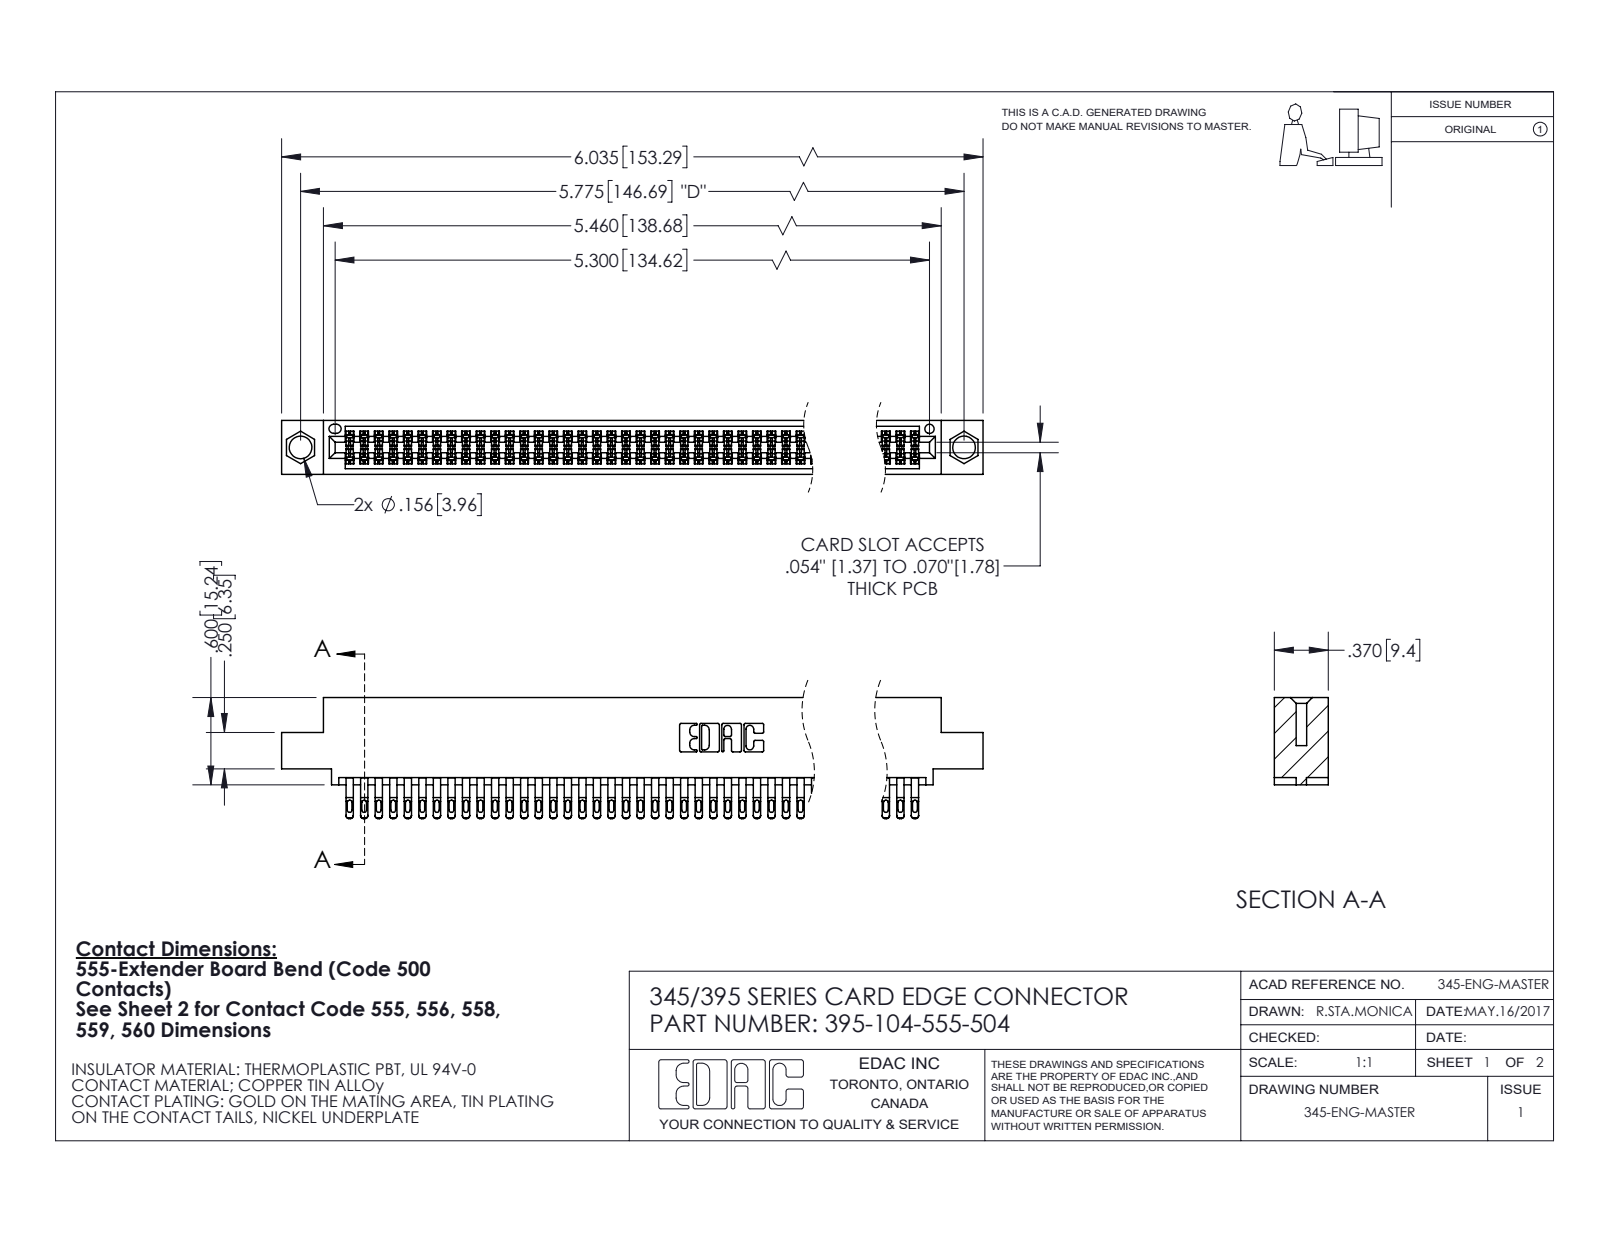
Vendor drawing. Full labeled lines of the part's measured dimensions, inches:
Part name (STEP PRODUCT): 395-104-555-504; 345 Part_0.110 Offset - 0.156 Dia-TI; 345-292-001_555 Tail
STEP written by: SolidWorks 2020 (CONFIG_CONTROL_DESIGN)
Units: inches
Bodies: 105 solids, 5968 faces (3322 planar, 2646 cylindrical, 0 other)
Overall size (bounding box): 6.035 × 0.832 × 0.37
Volume: 0.922 in³ · Surface area: 36.45 in²
Round holes (diameter × count): ⌀0.156 ×2, ⌀0.064 ×1
Partial cylindrical surfaces — rounded edges, fillets, slot ends (radius × count): R0.016 ×260, R0.006 ×208, R0.02 ×208, R0.01 ×22, R0.007 ×6, R0.031 ×6, R0.026 ×3, R0.01 ×2
Main face-to-face distances: 0.298, 0.072, 0.025, 0.37, 0.2, 0.098, 0.272, 0.225, 0.175, 0.149
Hole centre spacings: 0.27, 5.539, 5.775
